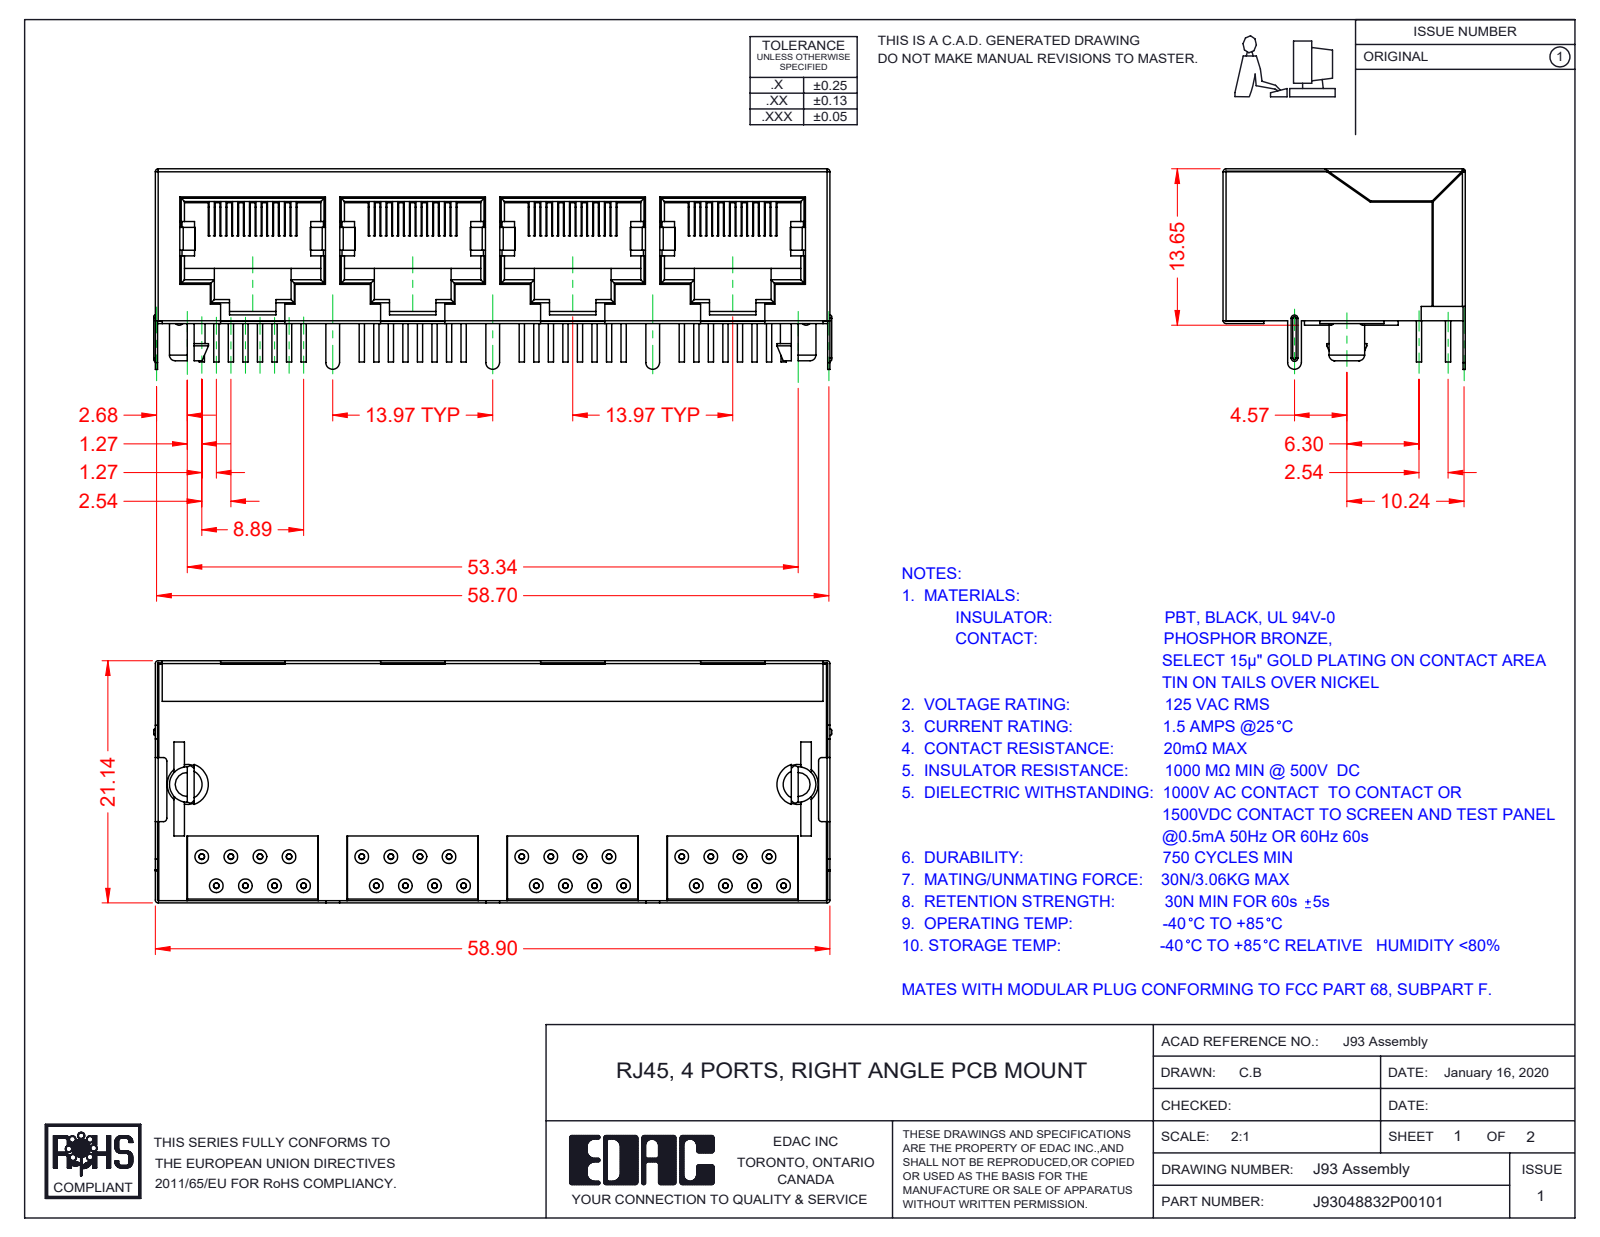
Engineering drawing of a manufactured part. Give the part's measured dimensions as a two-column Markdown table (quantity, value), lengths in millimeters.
| quantity | value |
| --- | --- |
| part name | 93 Contact Lock; RJ93048832P00101; 93 Insulator; 93 Contacts (+1 more) |
| STEP written by | SolidWorks 2016 (CONFIG_CONTROL_DESIGN) |
| units | millimeters |
| bodies | 38 solids, 2070 faces (1065 planar, 665 cylindrical, 340 other) |
| overall size | 59.2 × 21.14 × 17.5 |
| volume | 9 684 mm³ |
| surface area | 21 056 mm² |
| round holes (diameter × count) | 0.46 × 32 |
| round bosses / shafts (diameter × count) | 0.46 × 128, 3.1 × 2 |
| partial cylindrical surfaces (radius × count) | 0.3 × 22, 0.5 × 22, 0.19 × 16, 0.25 × 11, 0.15 × 4, 0.6 × 4, 0.4 × 2, 0.46 × 2 |
| main face-to-face distances | 0.8, 12.25, 12.2, 1, 0.75, 13.25, 13.05, 1.05, 0.85, 13 |
| hole center spacings | 2.84, 2.54, 13.97, 15.45, 12.95, 4.58, 16.51, 11.43 |
